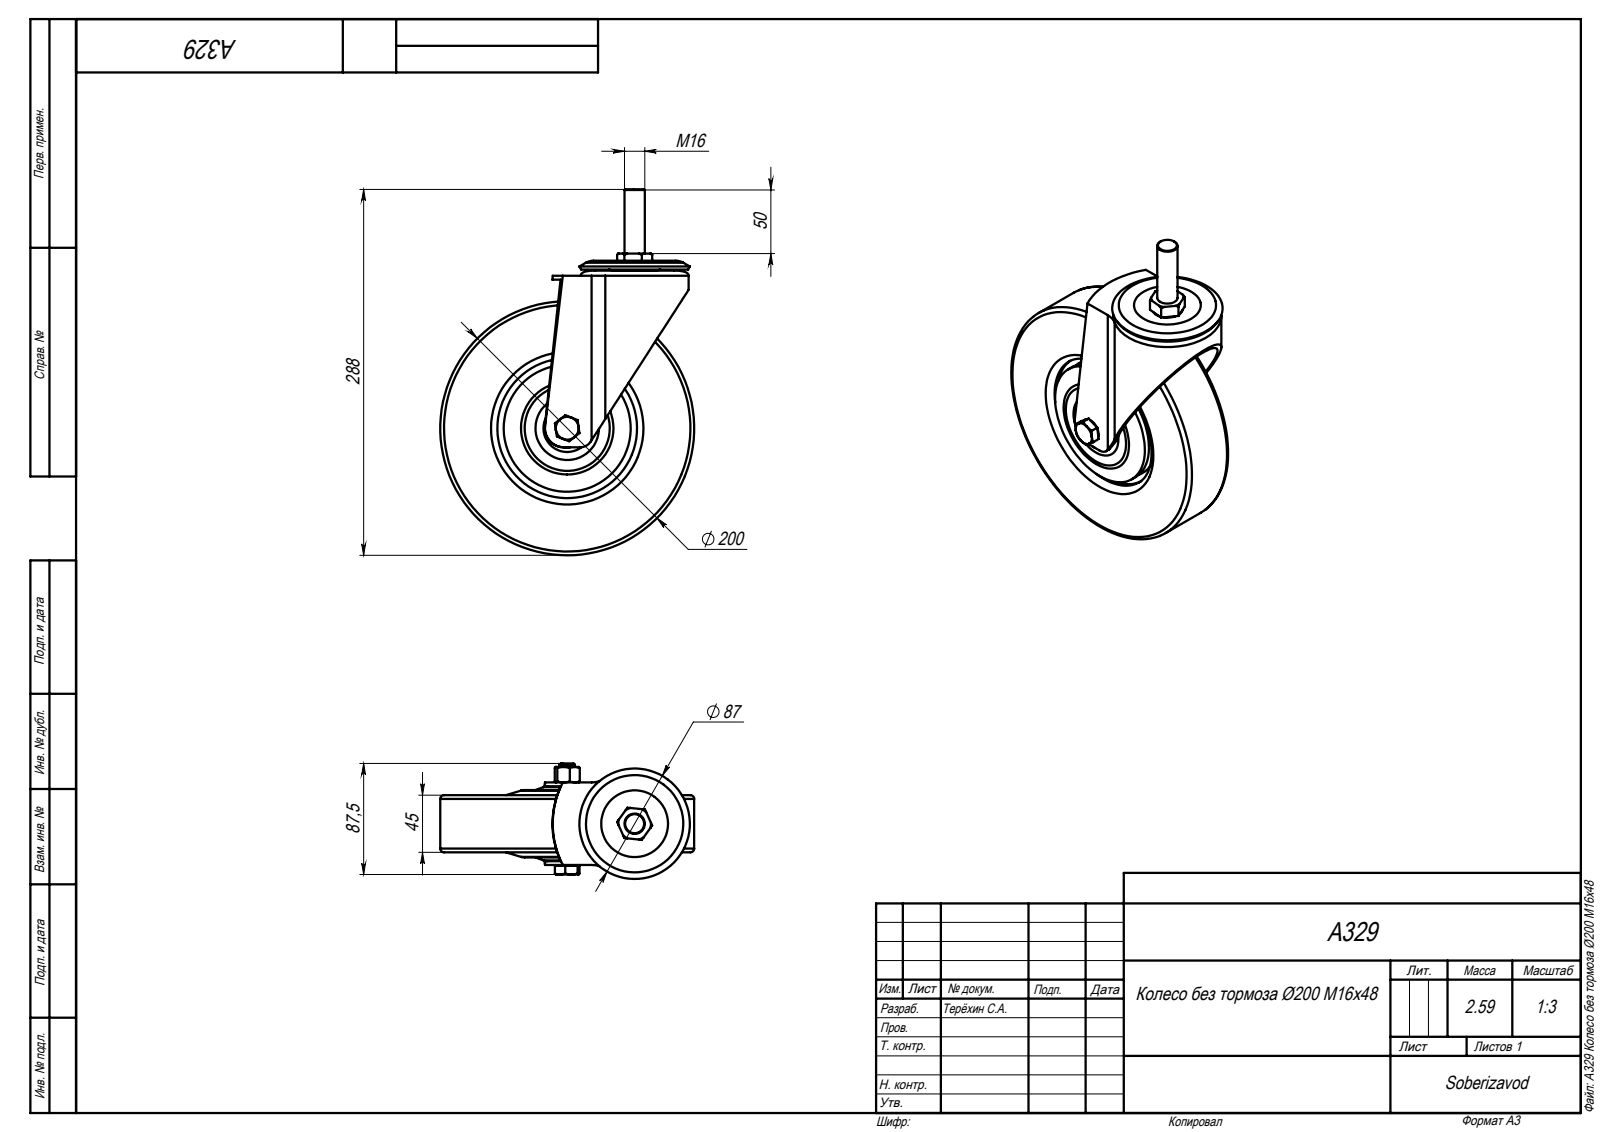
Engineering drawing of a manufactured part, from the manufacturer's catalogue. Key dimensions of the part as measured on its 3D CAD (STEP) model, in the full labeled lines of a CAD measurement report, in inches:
Part name (STEP PRODUCT): Колесо_00; Крышка_00; hex nut gradec_din_Hexagon Nut ISO 4034 - M12 - N; hex bolt gradeab_din_DIN EN 24014 - M12 x 80 x 30-N (+5 more)
STEP written by: SolidWorks 2018 (AUTOMOTIVE_DESIGN)
Units: inches
Bodies: 9 solids, 344 faces (149 planar, 50 cylindrical, 145 other)
Overall size (bounding box): 11.202 × 7.874 × 3.583
Volume: 72.13 in³ · Surface area: 335.9 in²
Round holes (diameter × count): ⌀0.472 ×2, ⌀0.315 ×1, ⌀0.402 ×1, ⌀3.78 ×1, ⌀4.331 ×1
Round bosses / shafts (diameter × count): ⌀7.874 ×1, ⌀3.937 ×1, ⌀0.709 ×1, ⌀0.63 ×1
Partial cylindrical surfaces — rounded edges, fillets, slot ends (radius × count): R0.787 ×2, R0.394 ×1, R1.555 ×1, R1.673 ×1
Main face-to-face distances: 1.575, 0.512, 1.063, 0.118, 0.886, 0.374, 1.437, 1.949, 2.323, 0.492
